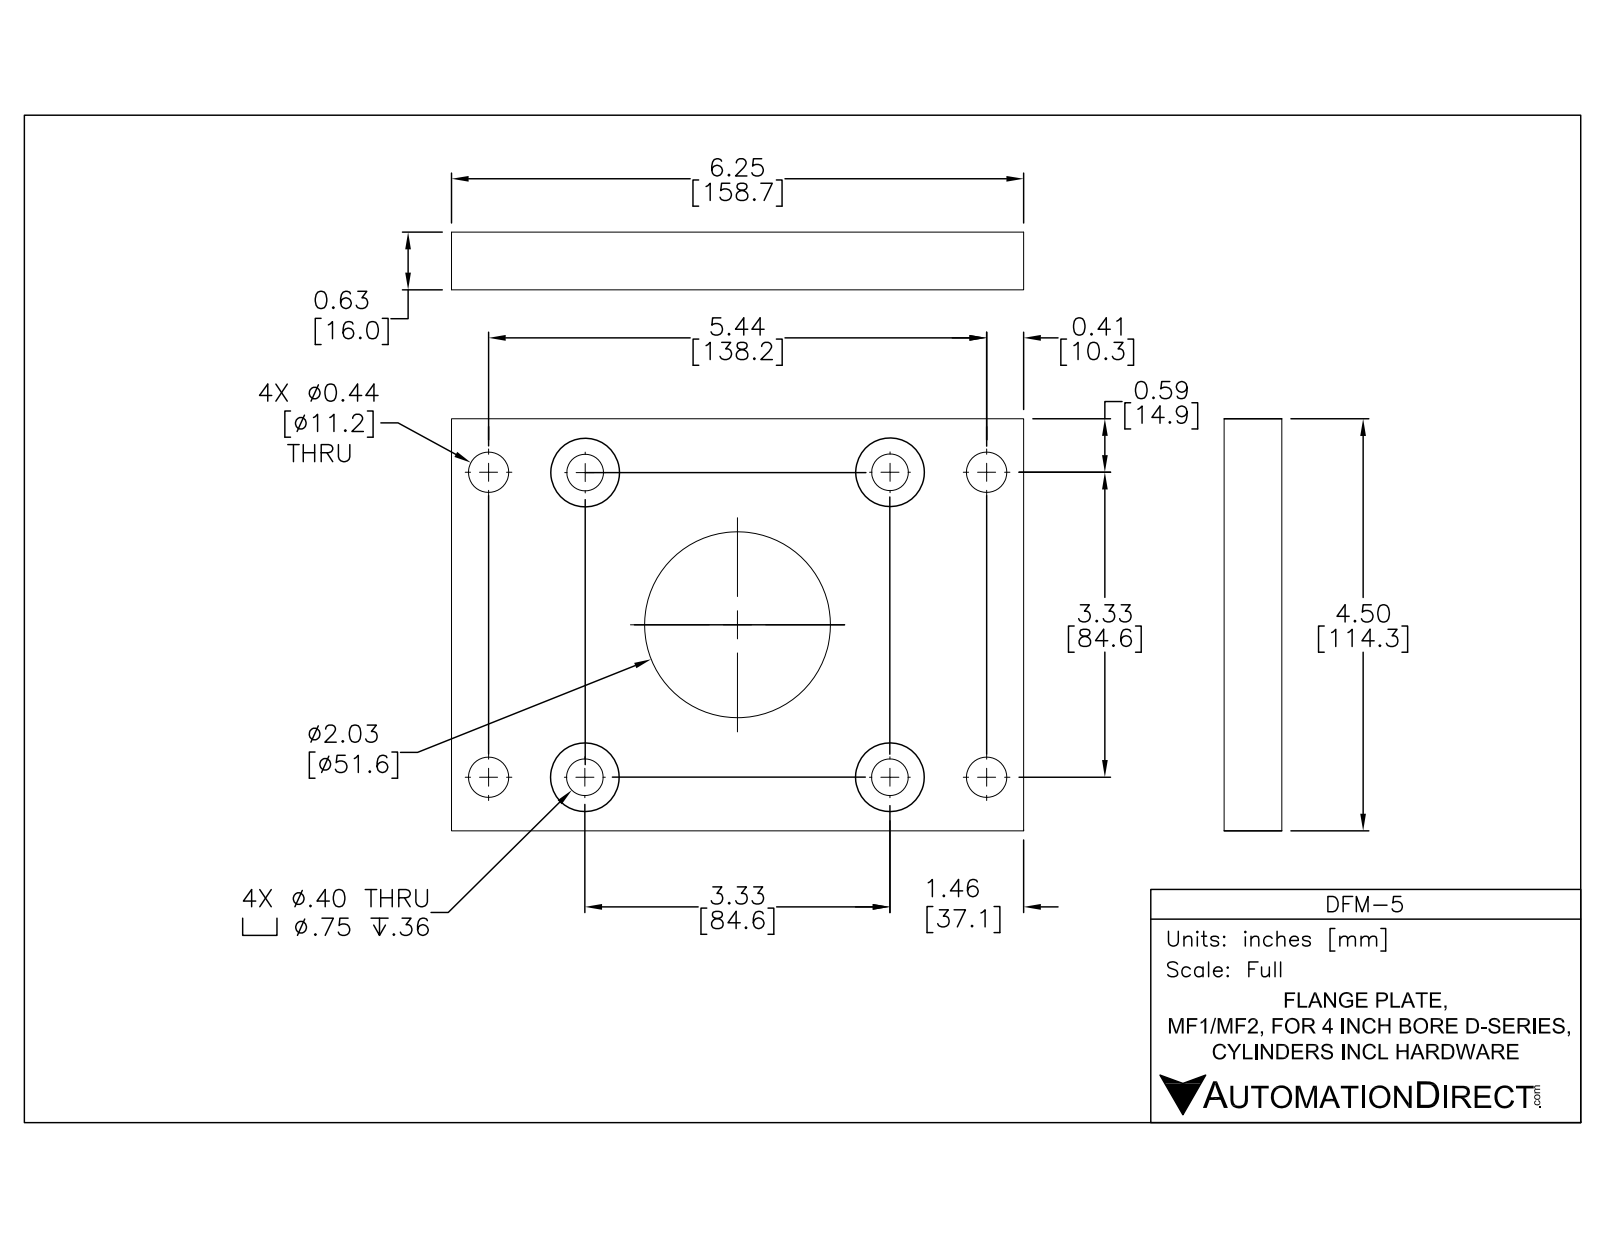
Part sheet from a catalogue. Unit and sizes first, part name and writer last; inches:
Units: inches
Overall size (bounding box): 6.25 × 4.5 × 0.625
Round holes (diameter × count): ⌀0.4 ×4, ⌀0.437 ×4, ⌀0.8 ×4, ⌀2.03 ×1
Main face-to-face distances: 0.625, 4.5, 6.25, 0.35, 0.275
Hole centre spacings: 3.328, 1.055, 2.354, 3.188, 3.491, 4.383, 5.504, 4.707
Volume: 14.34 in³ · Surface area: 73.33 in²
Bodies: 1 solid, 36 faces (10 planar, 26 cylindrical, 0 other)
Part name (STEP PRODUCT): DFM-5
STEP written by: SolidWorks 2015 (AUTOMOTIVE_DESIGN)
